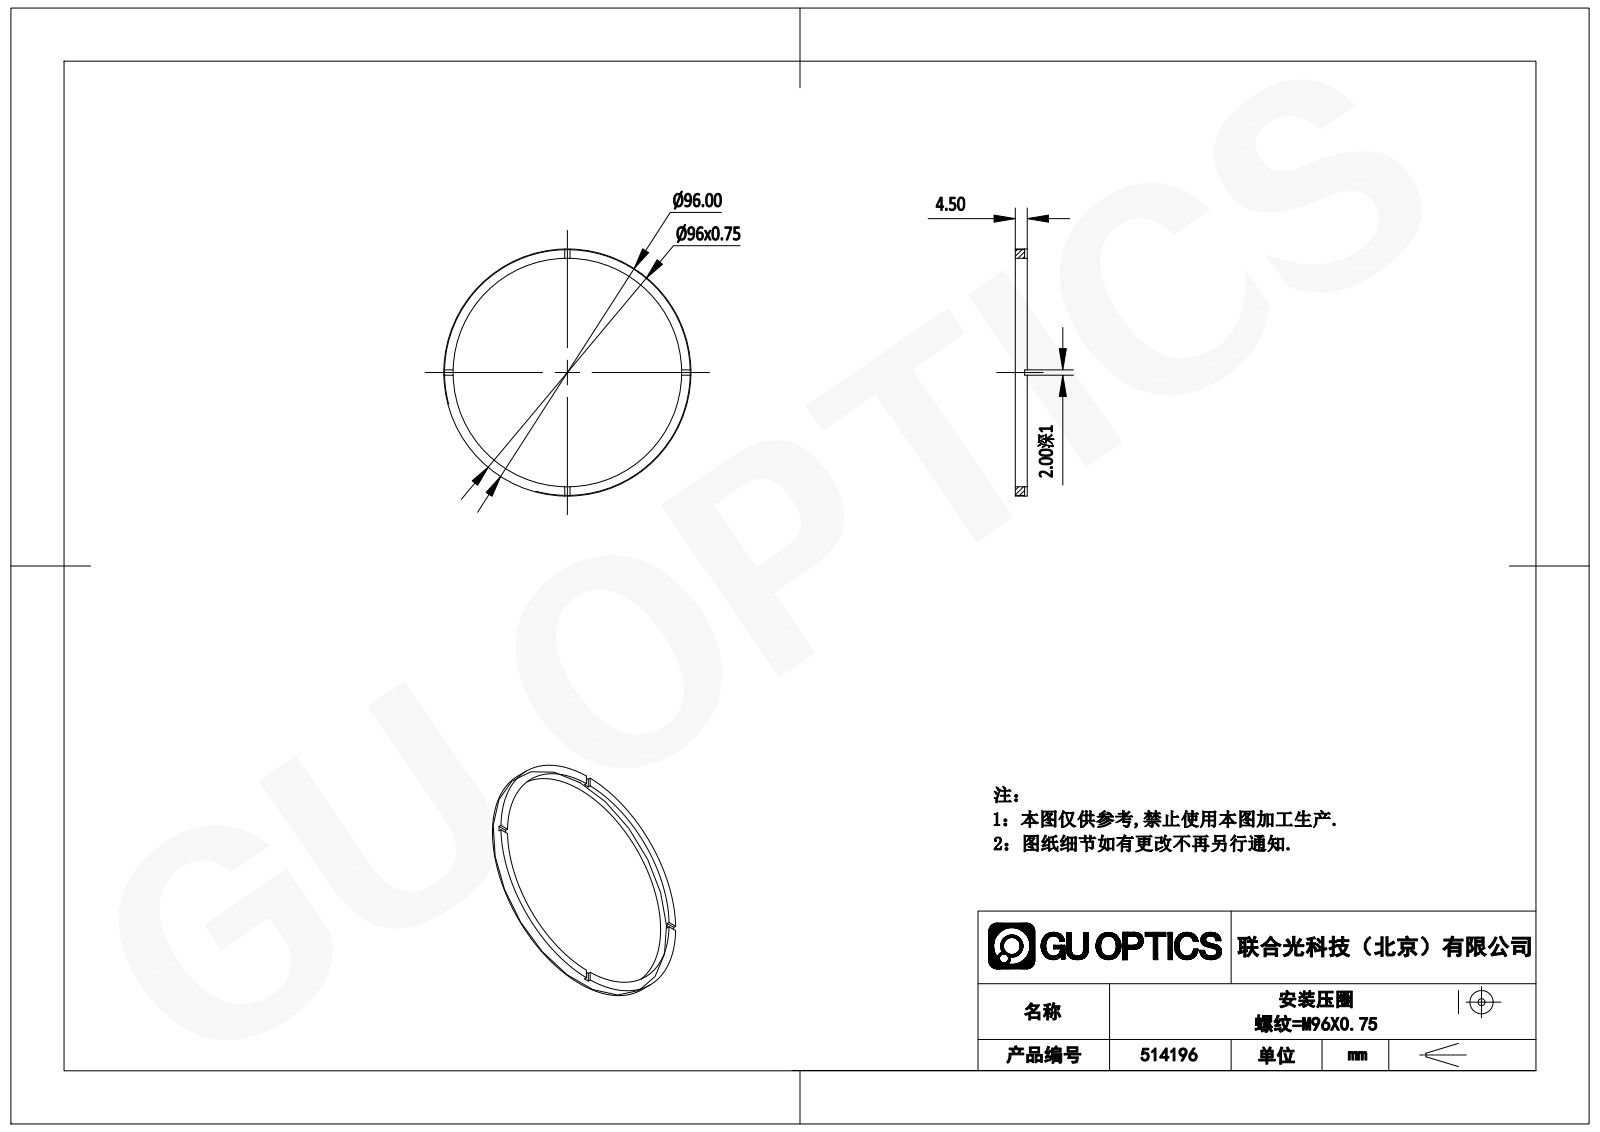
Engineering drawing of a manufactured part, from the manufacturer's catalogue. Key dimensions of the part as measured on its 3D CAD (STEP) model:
Part name (STEP PRODUCT): 514196
STEP written by: SolidWorks 2020 (CONFIG_CONTROL_DESIGN)
Units: millimetres
Bodies: 1 solid, 21 faces (17 planar, 4 cylindrical, 0 other)
Overall size (bounding box): 96 × 96 × 4.5
Volume: 4 549 mm³ · Surface area: 4 662 mm²
Round holes (diameter × count): ⌀89 ×1
Round bosses / shafts (diameter × count): ⌀96 ×1
Main face-to-face distances: 4.5, 3.5, 1, 2
